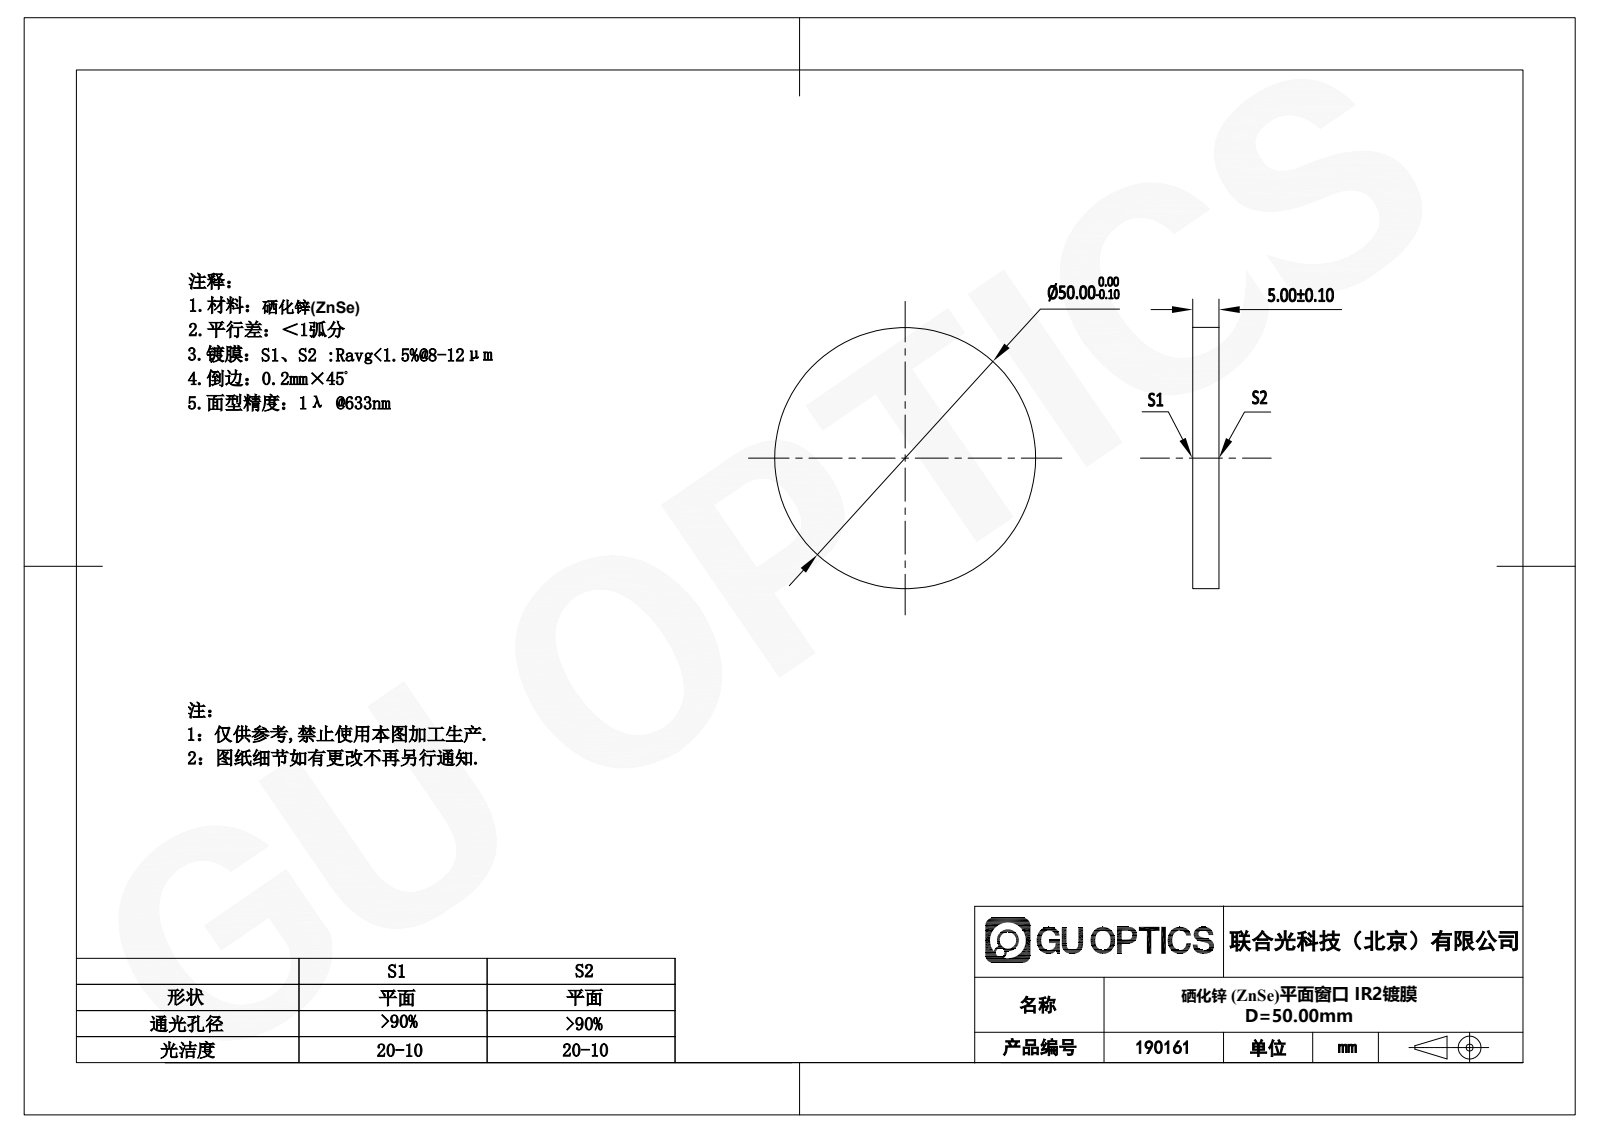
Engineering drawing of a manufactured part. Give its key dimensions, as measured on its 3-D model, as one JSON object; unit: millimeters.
{"part_name": "190160", "step_written_by": "SolidWorks 2016 (AUTOMOTIVE_DESIGN)", "units": "millimeters", "bodies": {"solids": 1, "faces": 4, "planar": 2, "cylindrical": 2, "other": 0}, "overall_size": [50, 50, 5], "volume_mm3": 9817, "surface_area_mm2": 4712, "round_bosses_or_shafts": [[50, 1]], "face_to_face_distances": [5]}
